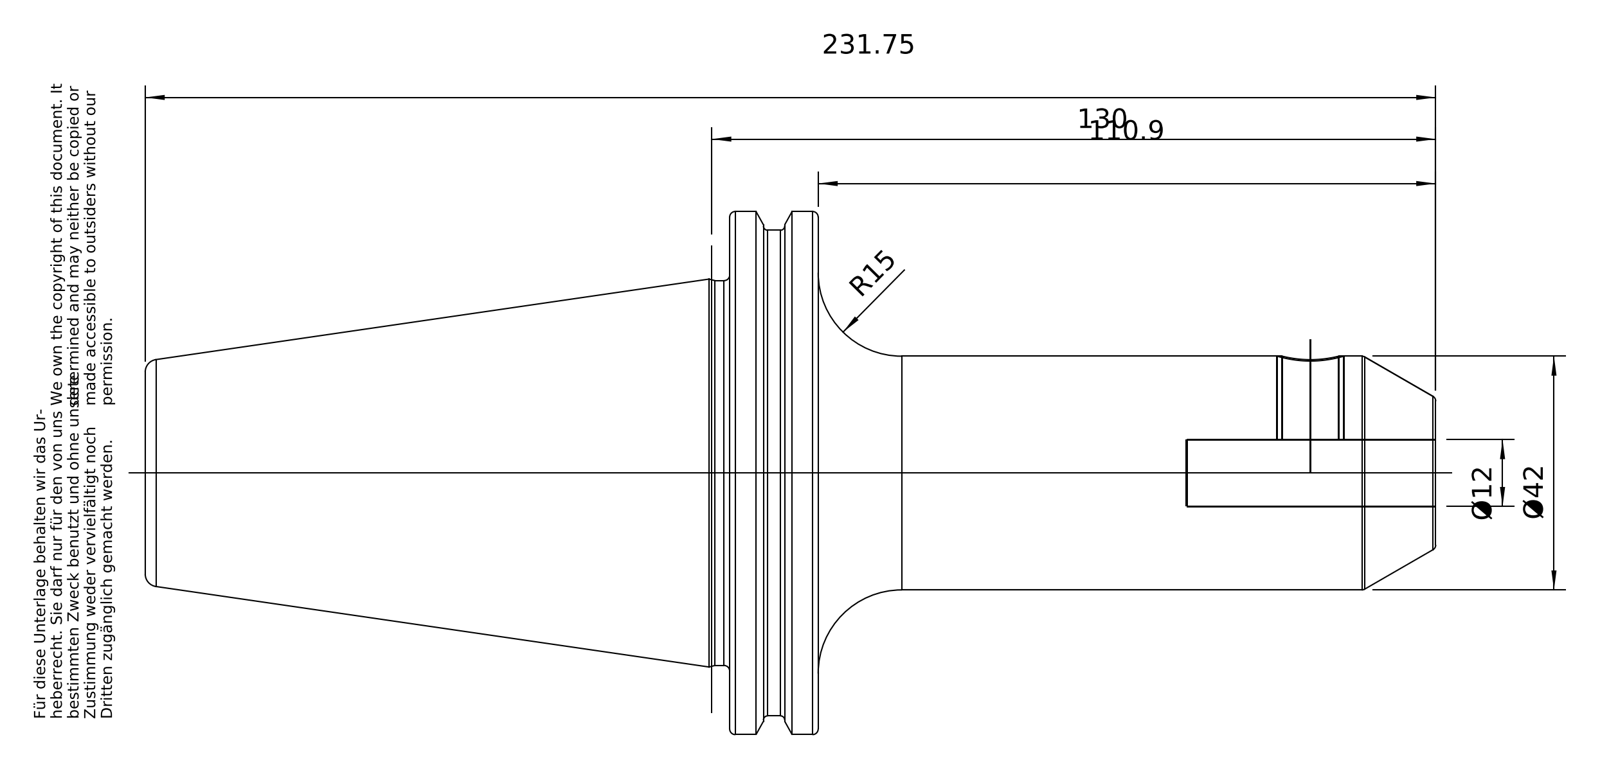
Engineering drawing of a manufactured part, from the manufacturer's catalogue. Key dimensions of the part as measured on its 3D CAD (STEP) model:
Part name (STEP PRODUCT): 50-304-12
STEP written by: PRO/ENGINEER BY PARAMETRIC TECHNOLOGY CORPORATION, 2010430 (CONFIG_CONTROL_DESIGN)
Units: millimetres
Bodies: 1 solid, 103 faces (21 planar, 32 cylindrical, 50 other)
Overall size (bounding box): 231.6 × 97.47 × 94
Volume: 488 594 mm³ · Surface area: 58 195 mm²
Round holes (diameter × count): ⌀12 ×2, ⌀10.2 ×1, ⌀20.75 ×1, ⌀25.01 ×1, ⌀25.7 ×1
Round bosses / shafts (diameter × count): ⌀91 ×1, ⌀69.15 ×1, ⌀42 ×1, ⌀24.01 ×1
Partial cylindrical surfaces — rounded edges, fillets, slot ends (radius × count): R1.75 ×5, R48.74 ×1
Main face-to-face distances: 15.85, 126.8, 110.95, 104.8, 120.65, 231.6, 72.8, 25.8, 48, 56.8
